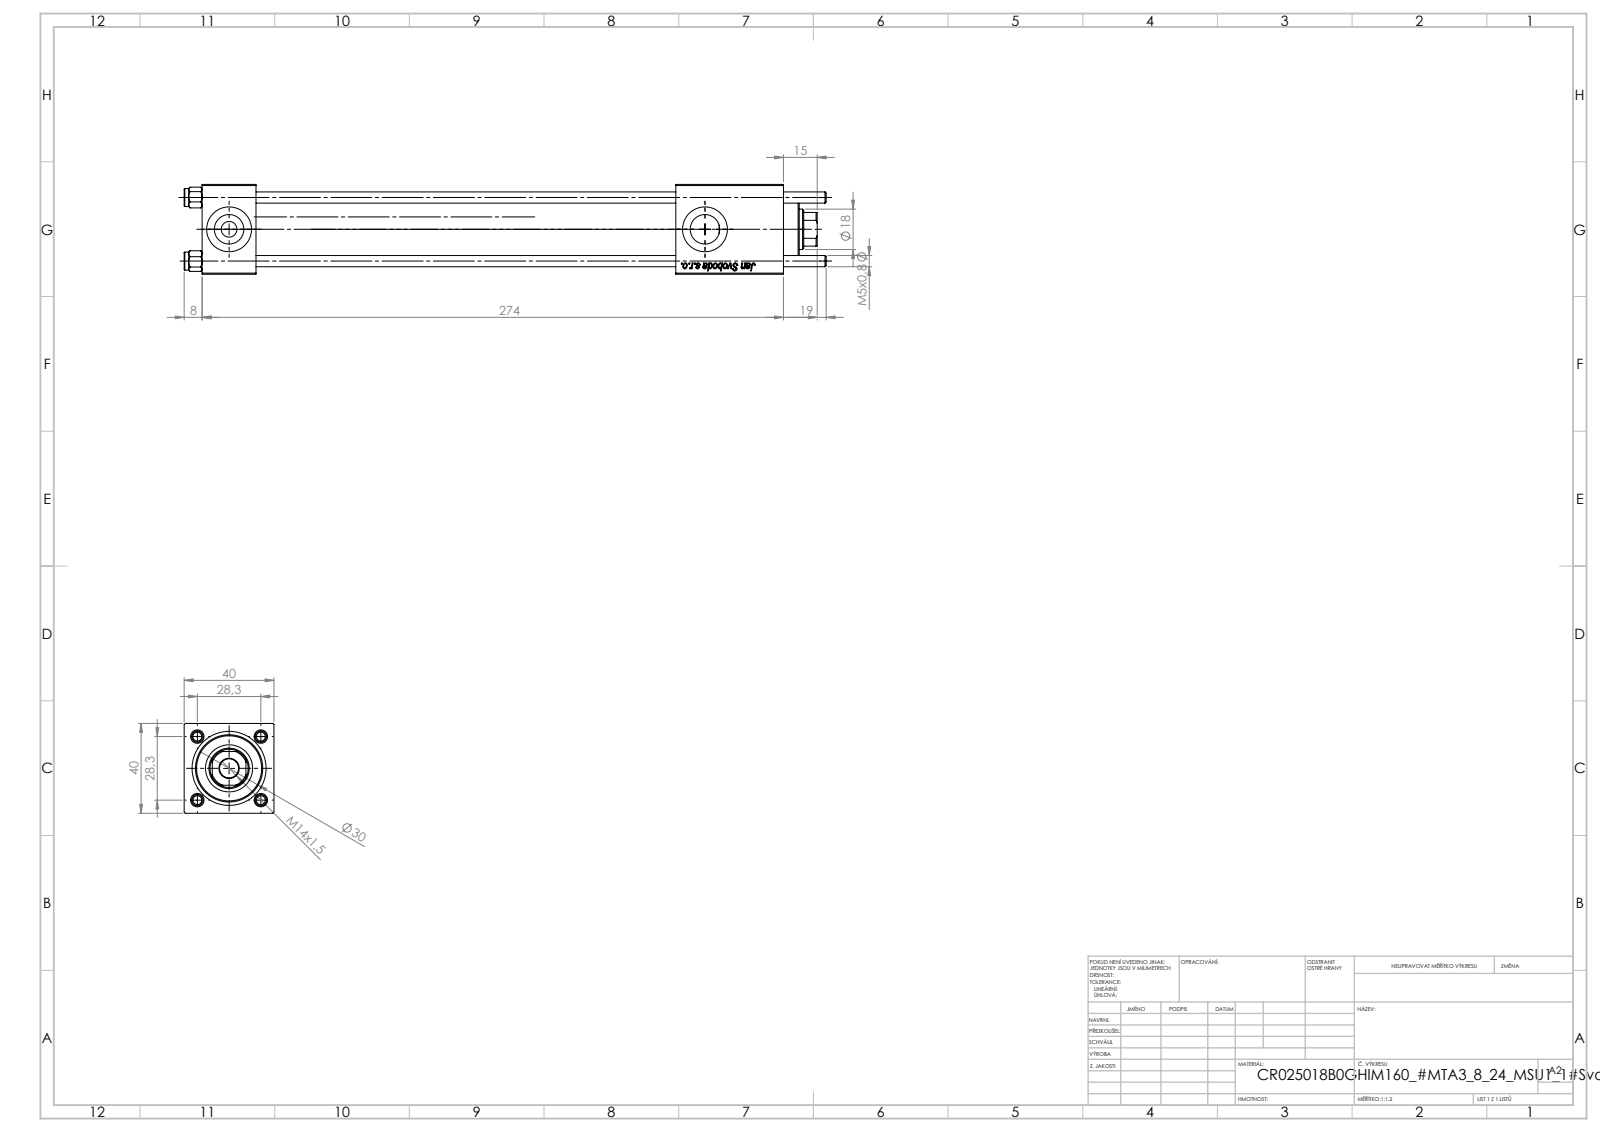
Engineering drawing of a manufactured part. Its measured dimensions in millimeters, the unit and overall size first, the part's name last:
Units: millimetres
Overall size (bounding box): 286 × 40 × 40
Round holes (diameter × count): ⌀5 ×4, ⌀20 ×3, ⌀7 ×2, ⌀13.16 ×2, ⌀8.5 ×1, ⌀18 ×1, ⌀21 ×1, ⌀25 ×1, ⌀30 ×1
Round bosses / shafts (diameter × count): ⌀8 ×4, ⌀31 ×1
Partial cylindrical surfaces — rounded edges, fillets, slot ends (radius × count): R8.5 ×1
Main face-to-face distances: 40, 24, 211, 187, 230.3, 206.3, 19.3, 259, 235, 48
Hole centre spacings: 20.01, 28.3, 40.02, 212
Volume: 236 057 mm³ · Surface area: 102 238 mm²
Bodies: 11 solids, 1152 faces (428 planar, 76 cylindrical, 648 other)
Part name (STEP PRODUCT): V215CR_B_TYCINKA; NUT_M5_B; V215_VC_A; V215CR_B-1 (+1 more)
STEP written by: SolidWorks 2019 (CONFIG_CONTROL_DESIGN)
